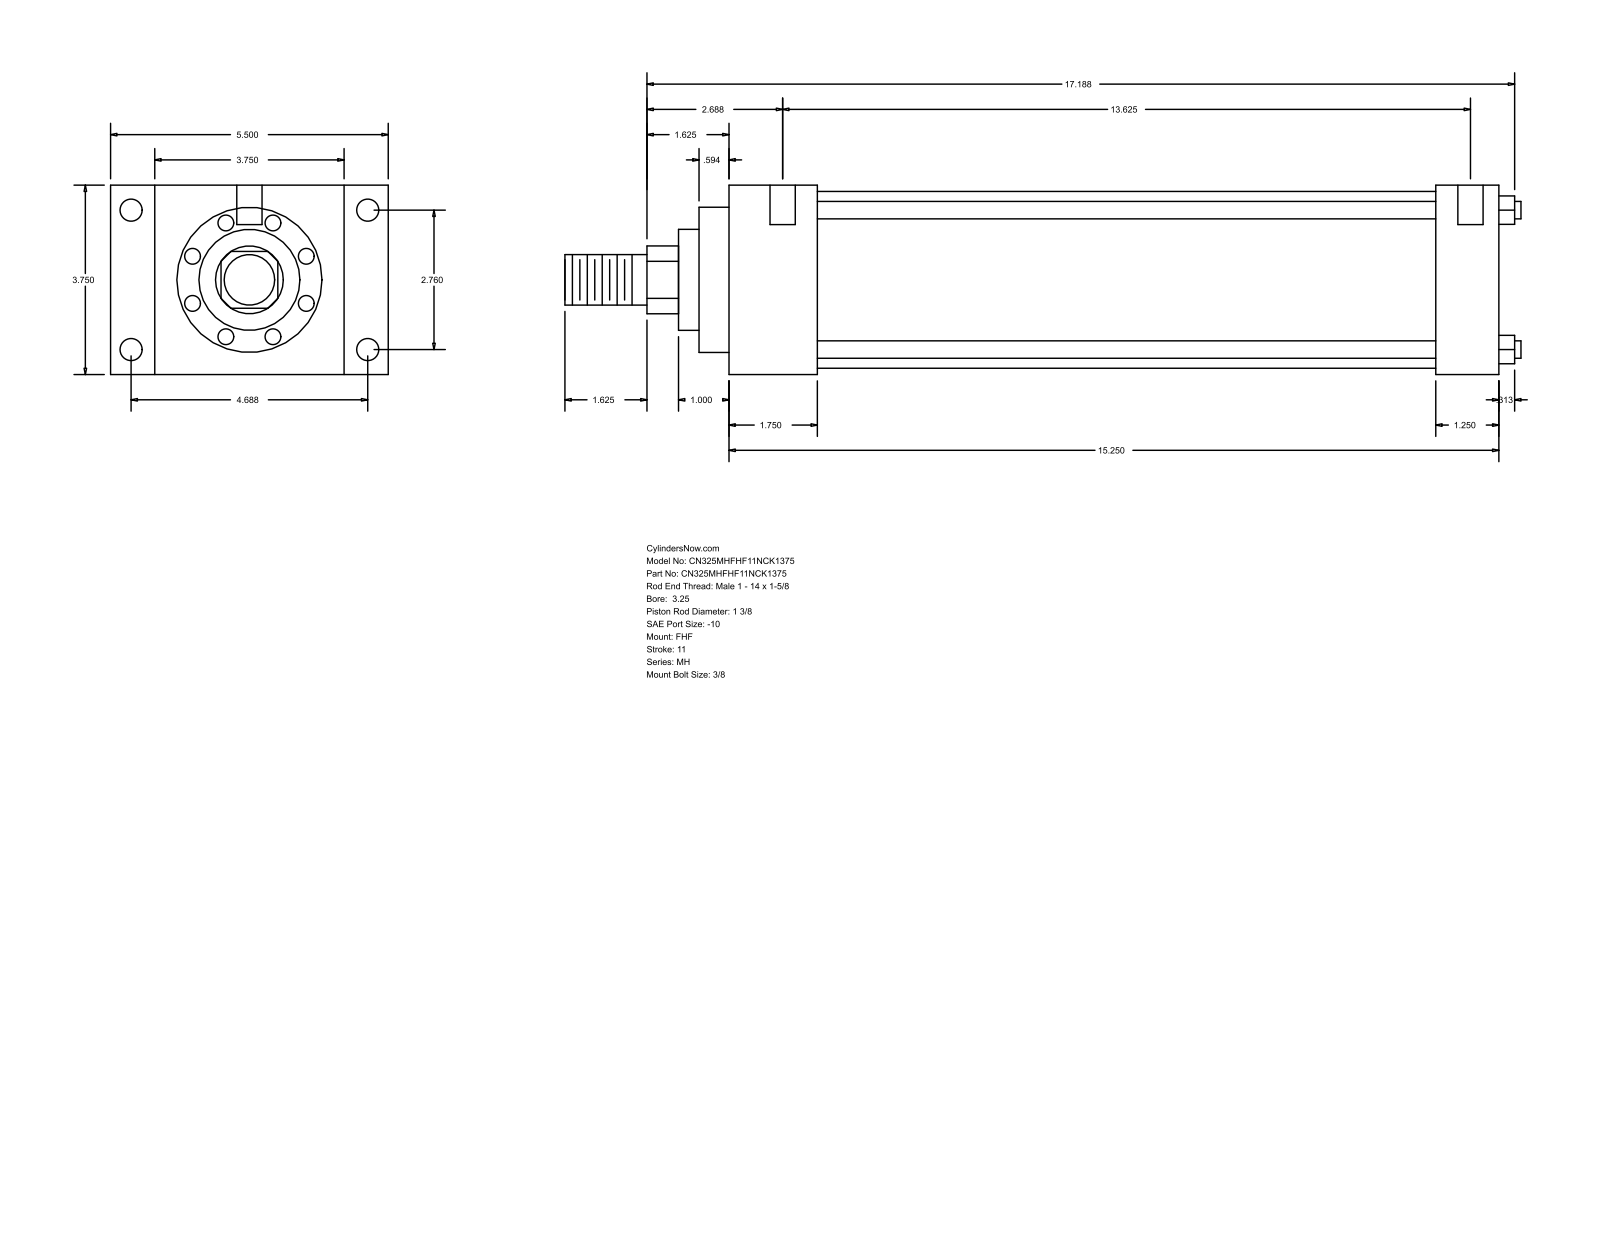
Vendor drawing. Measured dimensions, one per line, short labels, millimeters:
name: MH_FHF__0325_1.375
written by: GSSL Pune (CONFIG_CONTROL_DESIGN)
unit: mm
bodies: 0 solids, 90 faces (61 planar, 29 cylindrical, 0 other)
size: 481.01 × 139.7 × 95.25
holes: 4× ⌀5.56, 4× ⌀11.13, 2× ⌀12.7
bosses: 4× ⌀8.76, 1× ⌀88.9, 1× ⌀73.03, 1× ⌀50.8, 1× ⌀34.92, 1× ⌀25.4
rounds: 1× R17.06
face distances: 95.24, 387.35, 44.45, 342.9, 22.23, 117.47, 139.7, 355.61, 311.16, 31.74
hole spacings: 70.1, 119.06, 138.16, 352.43, 1.59, 4.76, 346.08, 347.67
